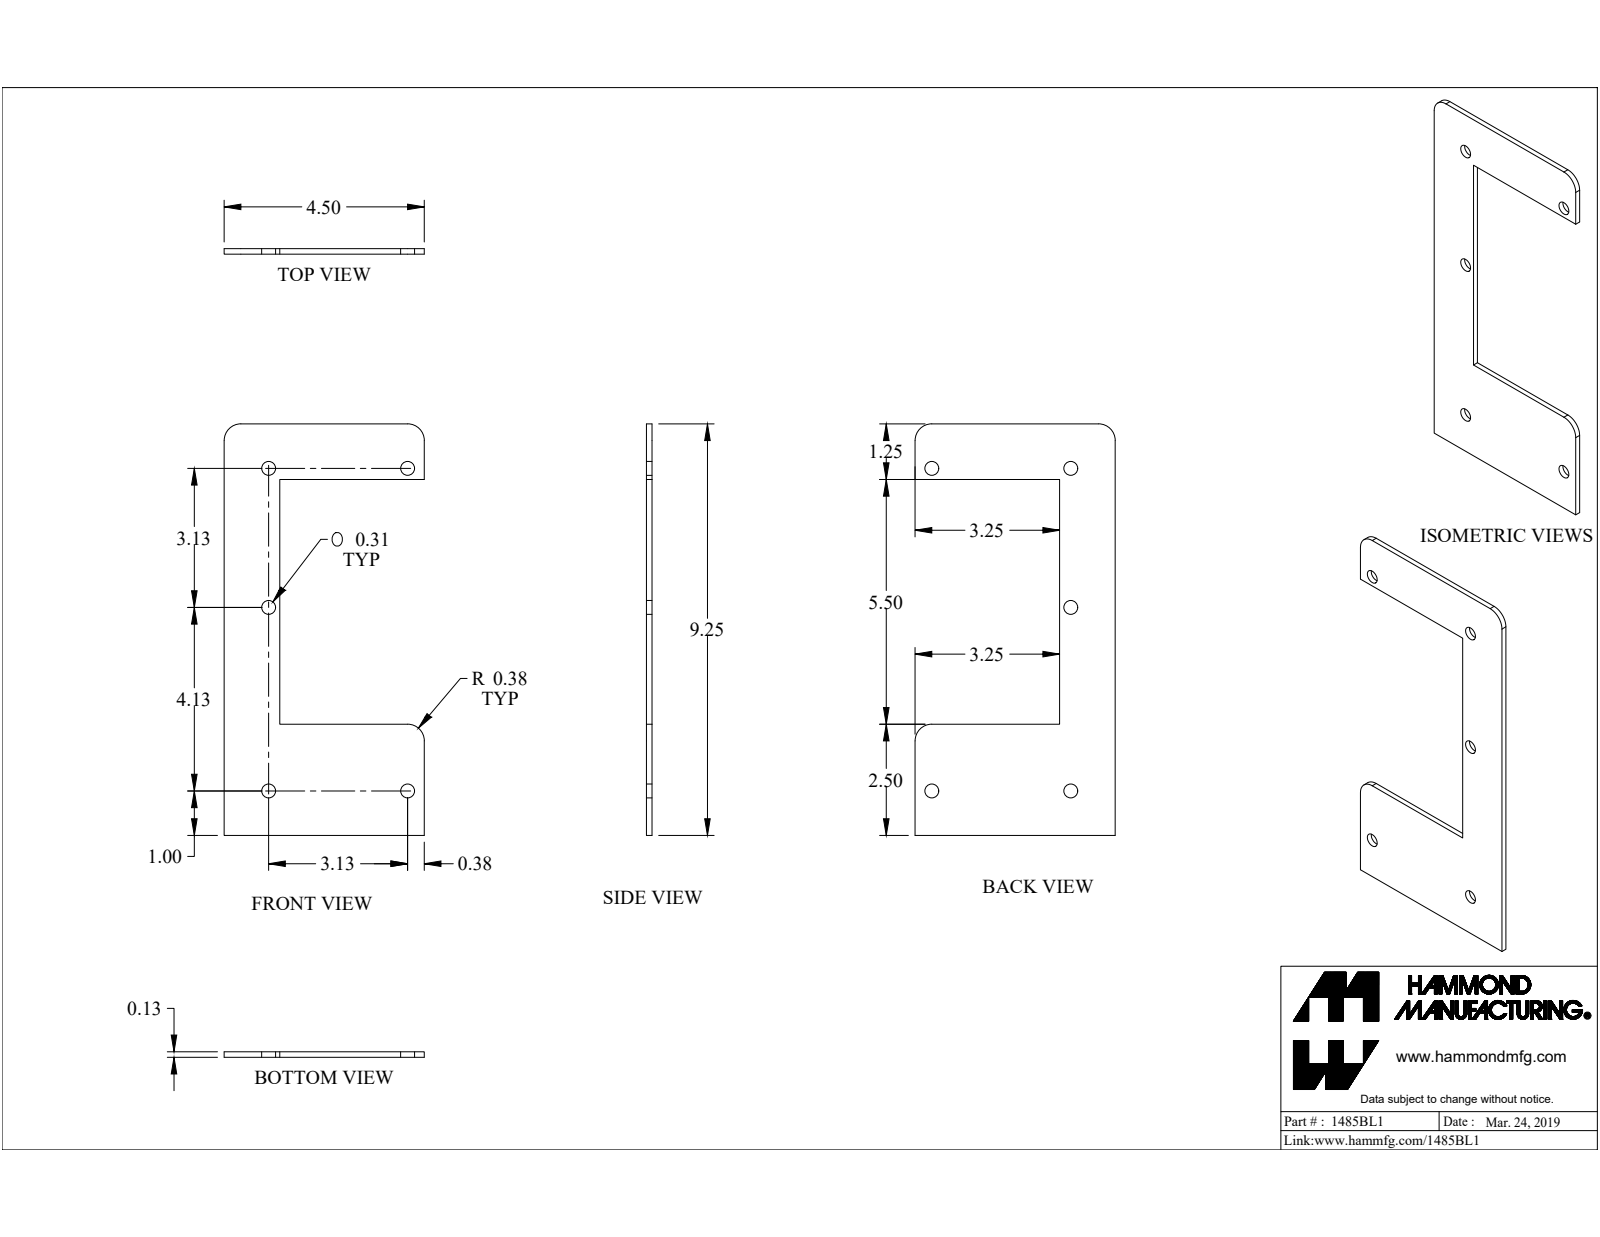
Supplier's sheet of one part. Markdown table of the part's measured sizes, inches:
| quantity | value |
| --- | --- |
| part name | 1485BL1 |
| STEP written by | SolidWorks 2019 (CONFIG_CONTROL_DESIGN) |
| units | inches |
| bodies | 1 solid, 18 faces (10 planar, 8 cylindrical, 0 other) |
| overall size | 9.25 × 4.5 × 0.125 |
| volume | 2.909 in³ |
| surface area | 51.36 in² |
| round holes (diameter × count) | 0.313 × 5 |
| partial cylindrical surfaces (radius × count) | 0.375 × 3 |
| main face-to-face distances | 0.125, 1.25, 9.25, 8, 4.5, 3.25, 6.75, 5.5, 2.5 |
| hole center spacings | 3.125, 7.25, 7.895, 4.125, 4.419, 5.175 |
